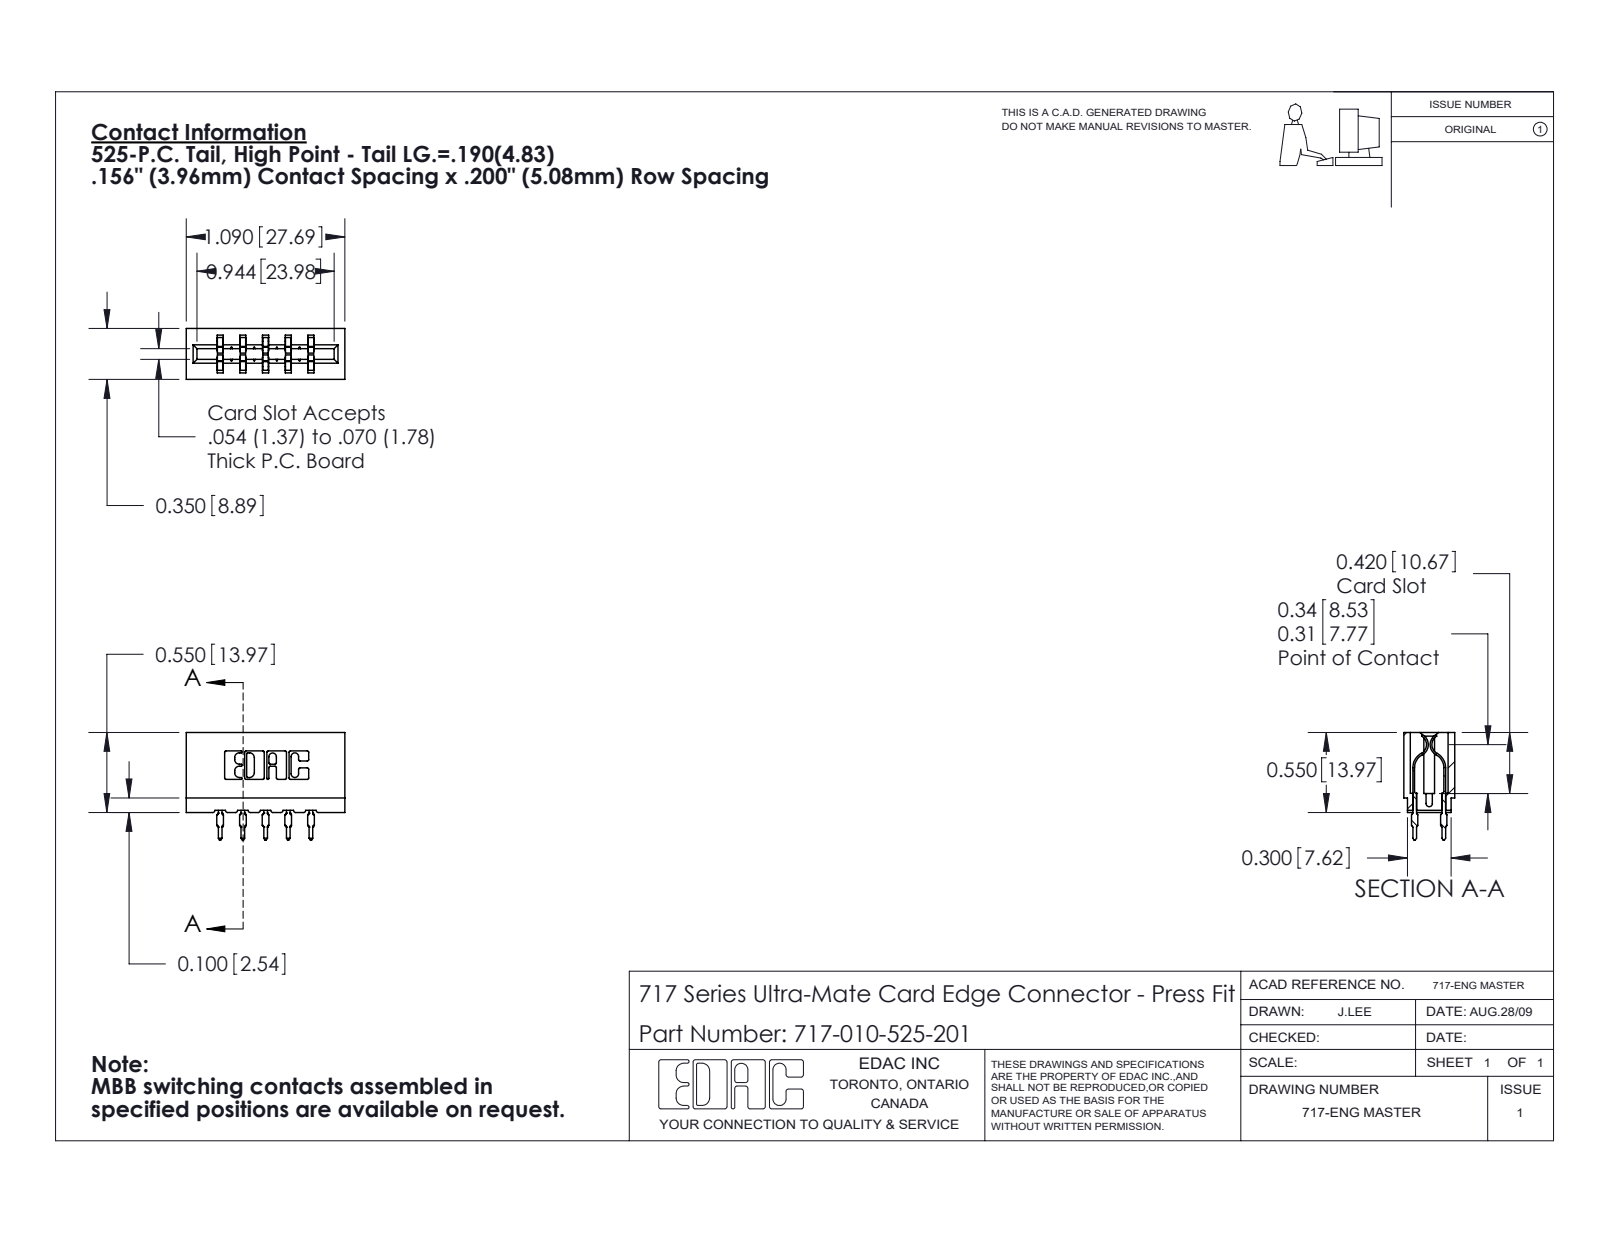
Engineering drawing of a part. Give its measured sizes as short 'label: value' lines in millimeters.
name: 745-292-001_525; 717-010-525-201; 717 Part_Insulator Option - 06
written by: SolidWorks 2020 (CONFIG_CONTROL_DESIGN)
unit: mm
bodies: 11 solids, 994 faces (519 planar, 215 cylindrical, 260 other)
size: 27.7 × 18.8 × 8.9
volume: 2 560 mm³; area: 3 392 mm²
rounds: 22× R0.3, 20× R0.5, 10× R0.4, 8× R0.1, 8× R0.3, 6× R0.2, 6× R0.8, 3× R0.7
face distances: 5.4, 4, 3.5, 8.9, 5, 1.1, 7.9, 7.9, 11.9, 1.9
